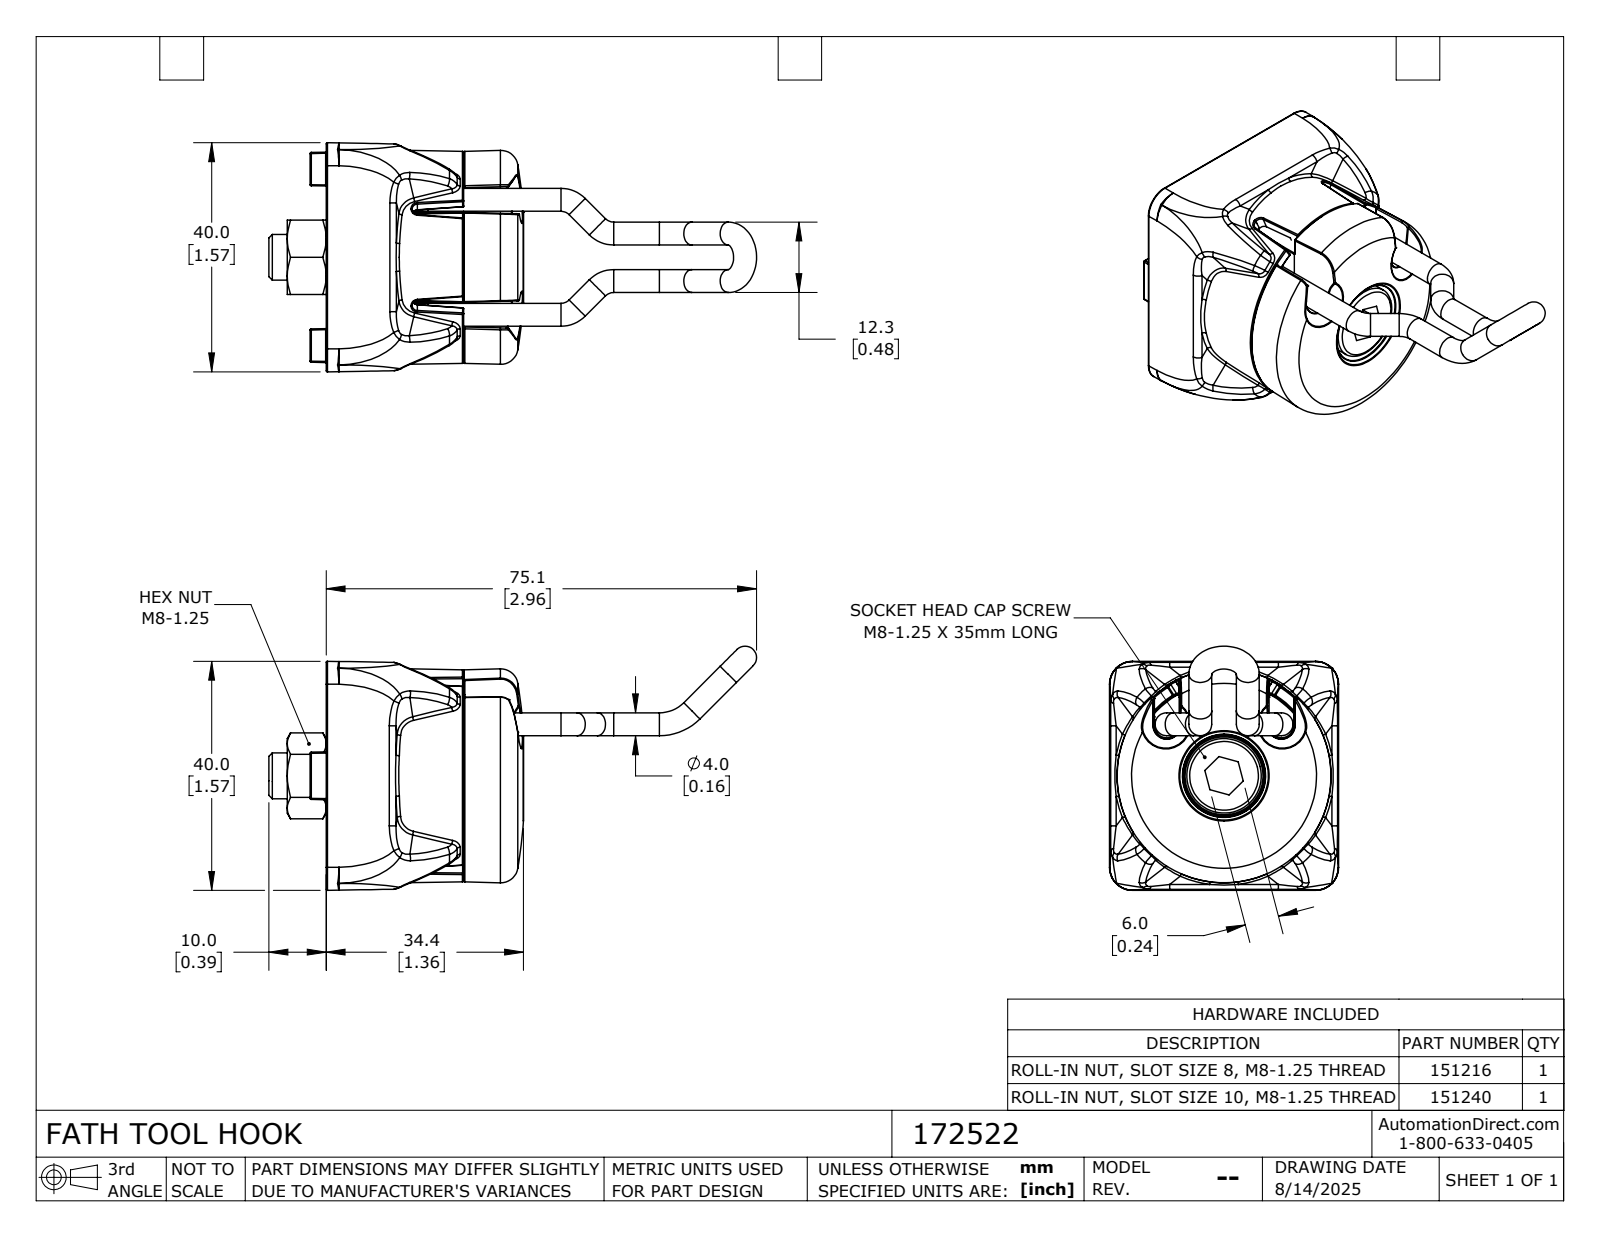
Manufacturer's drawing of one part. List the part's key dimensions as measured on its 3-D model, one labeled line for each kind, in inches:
Part name (STEP PRODUCT): 172522
STEP written by: SolidWorks 2024 (CONFIG_CONTROL_DESIGN)
Units: inches
Bodies: 7 solids, 1255 faces (228 planar, 313 cylindrical, 714 other)
Overall size (bounding box): 3.352 × 1.679 × 1.575
Volume: 2.447 in³ · Surface area: 33.07 in²
Round holes (diameter × count): ⌀0.268 ×1, ⌀0.315 ×1, ⌀0.512 ×1
Round bosses / shafts (diameter × count): ⌀0.157 ×12, ⌀0.512 ×1
Partial cylindrical surfaces — rounded edges, fillets, slot ends (radius × count): R0.008 ×146, R0.02 ×22, R0.039 ×8, R0.157 ×8, R0.047 ×4, R0.085 ×2, R0.657 ×1
Main face-to-face distances: 0.531, 1.213, 0.315, 0.236, 0.524, 0.669, 0.421, 0.945, 0.413, 0.63
